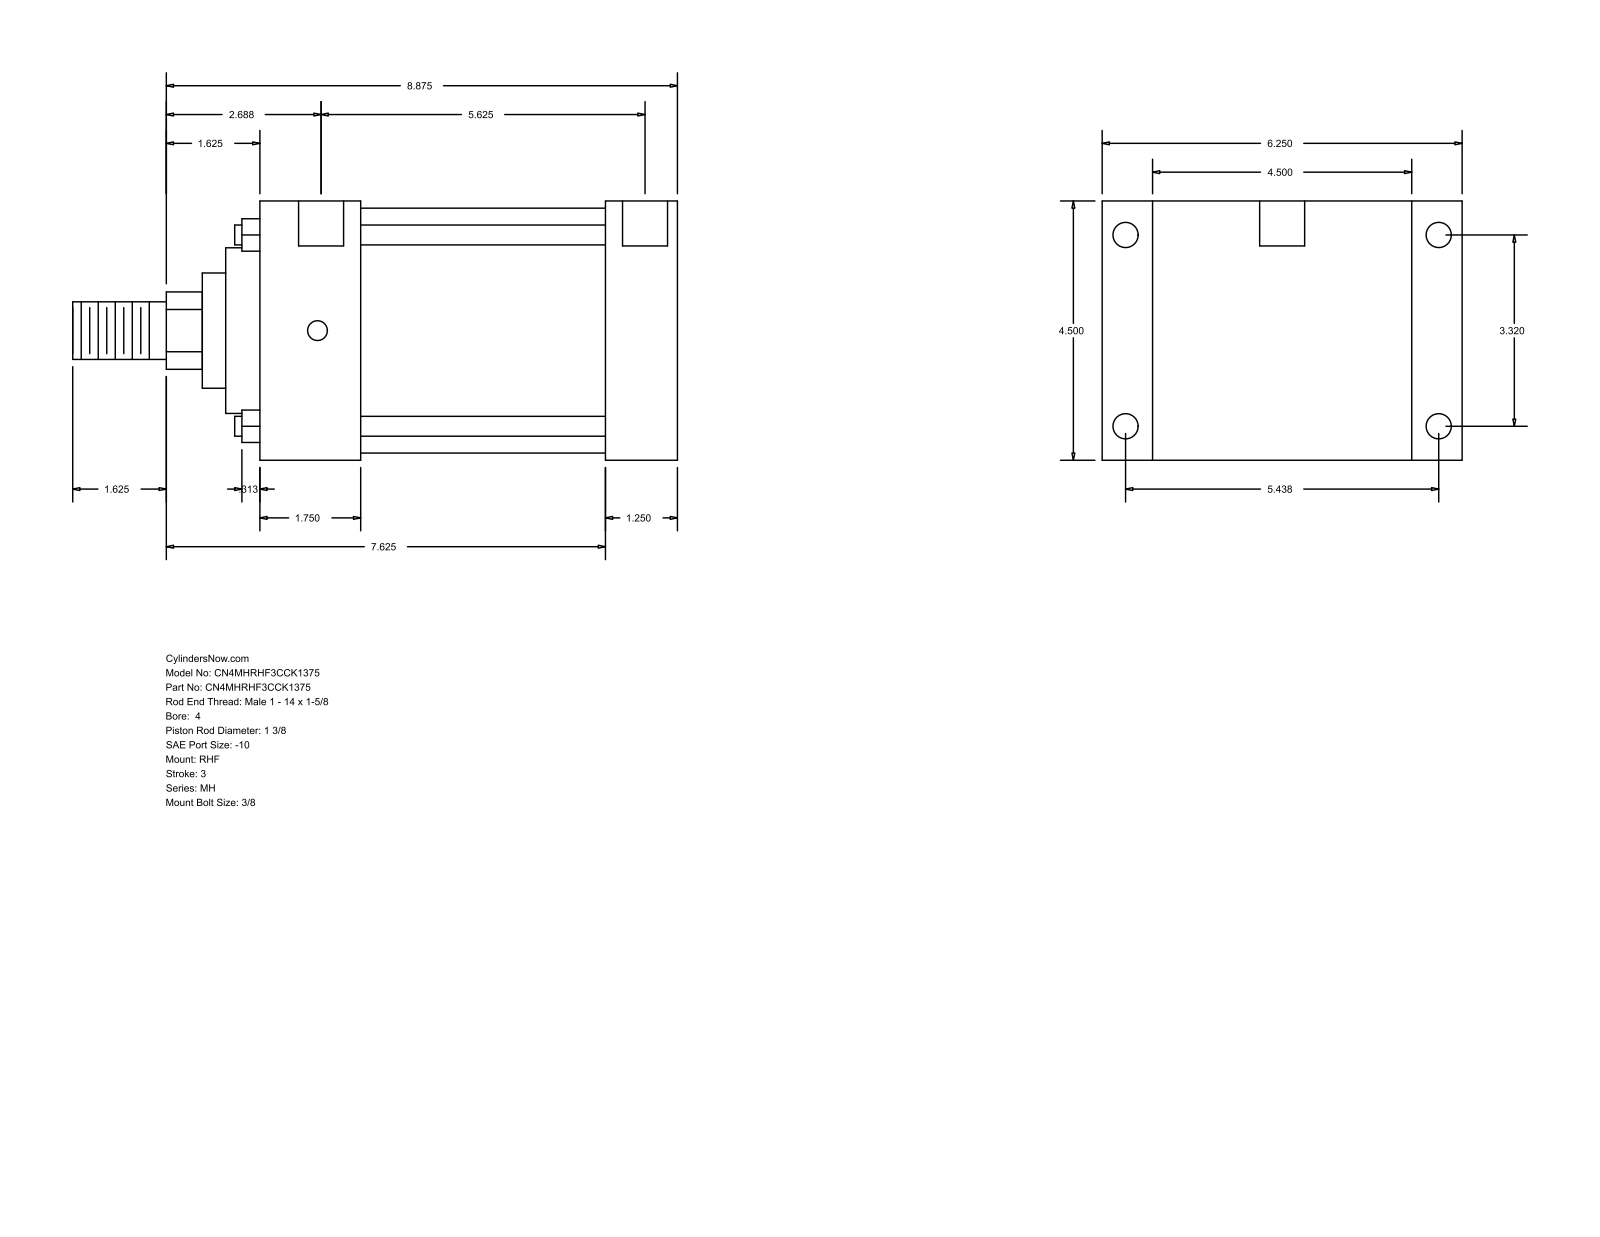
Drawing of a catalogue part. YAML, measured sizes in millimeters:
part_name: "MH_RHF__0400_1.375"
step_written_by: "GSSL Pune (CONFIG_CONTROL_DESIGN)"
units: millimeters
bodies: {solids: 0, faces: 90, planar: 61, cylindrical: 29, other: 0}
overall_size: [266.7, 158.75, 114.3]
round_holes:
  - {diameter: 8.73, count: 4}
  - {diameter: 11.13, count: 4}
  - {diameter: 19.84, count: 2}
round_bosses_or_shafts:
  - {diameter: 8.76, count: 4}
  - {diameter: 107.95, count: 1}
  - {diameter: 73.03, count: 1}
  - {diameter: 50.8, count: 1}
  - {diameter: 34.92, count: 1}
  - {diameter: 25.4, count: 1}
partial_cylinders:
  - {radius: 17.06, count: 1}
face_to_face_distances: [114.3, 31.75, 152.41, 184.16, 22.23, 136.53, 44.45, 107.96, 139.71, 158.76]
hole_center_spacings: [84.32, 138.12, 146.05, 161.82, 1.58, 1.59, 142.88, 144.46]
